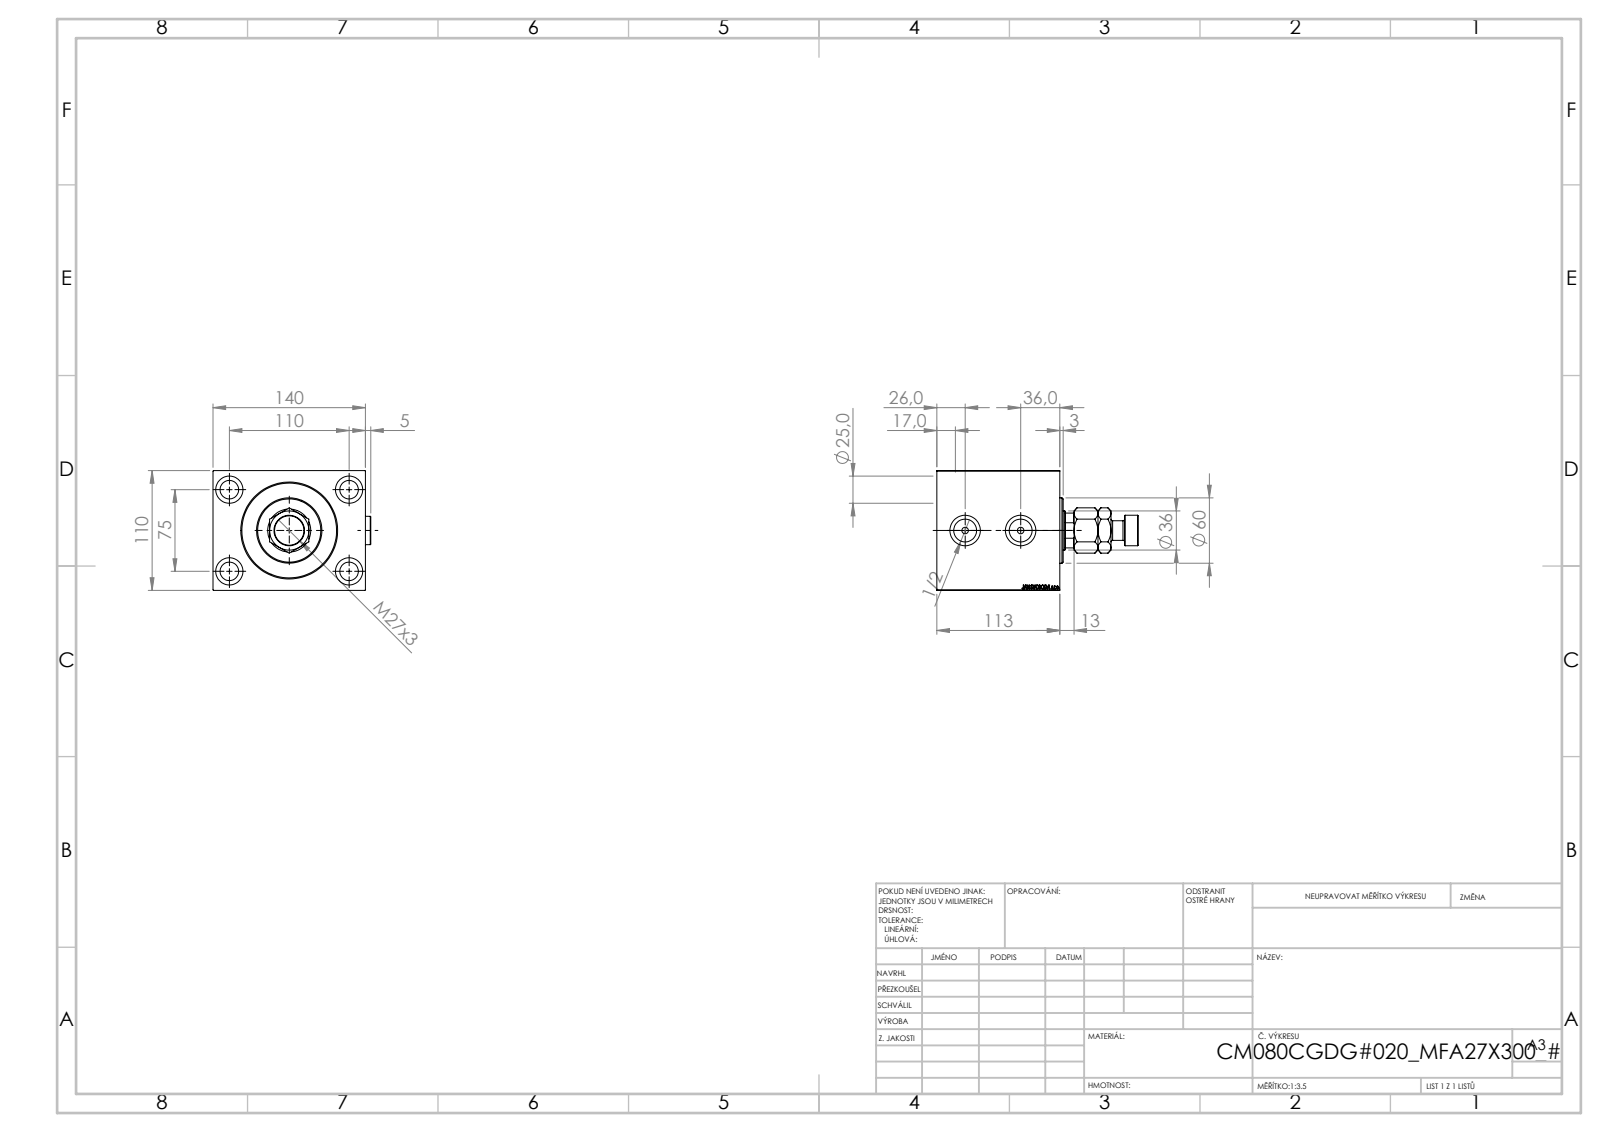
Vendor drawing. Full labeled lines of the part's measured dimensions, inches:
Part name (STEP PRODUCT): MFA; Zatka_OIL_PORT; V450CM_C_VCP; V450CM_VC_B (+1 more)
STEP written by: SolidWorks 2019 (CONFIG_CONTROL_DESIGN)
Units: inches
Bodies: 6 solids, 969 faces (459 planar, 80 cylindrical, 430 other)
Overall size (bounding box): 7.283 × 5.705 × 4.331
Volume: 97.15 in³ · Surface area: 287 in²
Round holes (diameter × count): ⌀0.669 ×4, ⌀0.984 ×4, ⌀0.236 ×2, ⌀0.825 ×2, ⌀1.102 ×2, ⌀1.004 ×1, ⌀1.417 ×1, ⌀1.555 ×1, ⌀3.15 ×1, ⌀3.228 ×1, ⌀3.425 ×1
Round bosses / shafts (diameter × count): ⌀1.024 ×2, ⌀2.362 ×1, ⌀1.102 ×1, ⌀0.709 ×1
Partial cylindrical surfaces — rounded edges, fillets, slot ends (radius × count): R0.689 ×1
Main face-to-face distances: 4.331, 5.512, 4.449, 2.008, 2.441, 0.394, 0.85, 1.157, 3.598, 1.244
Hole centre spacings: 2.621, 2.953, 4.331, 5.242, 2.008
